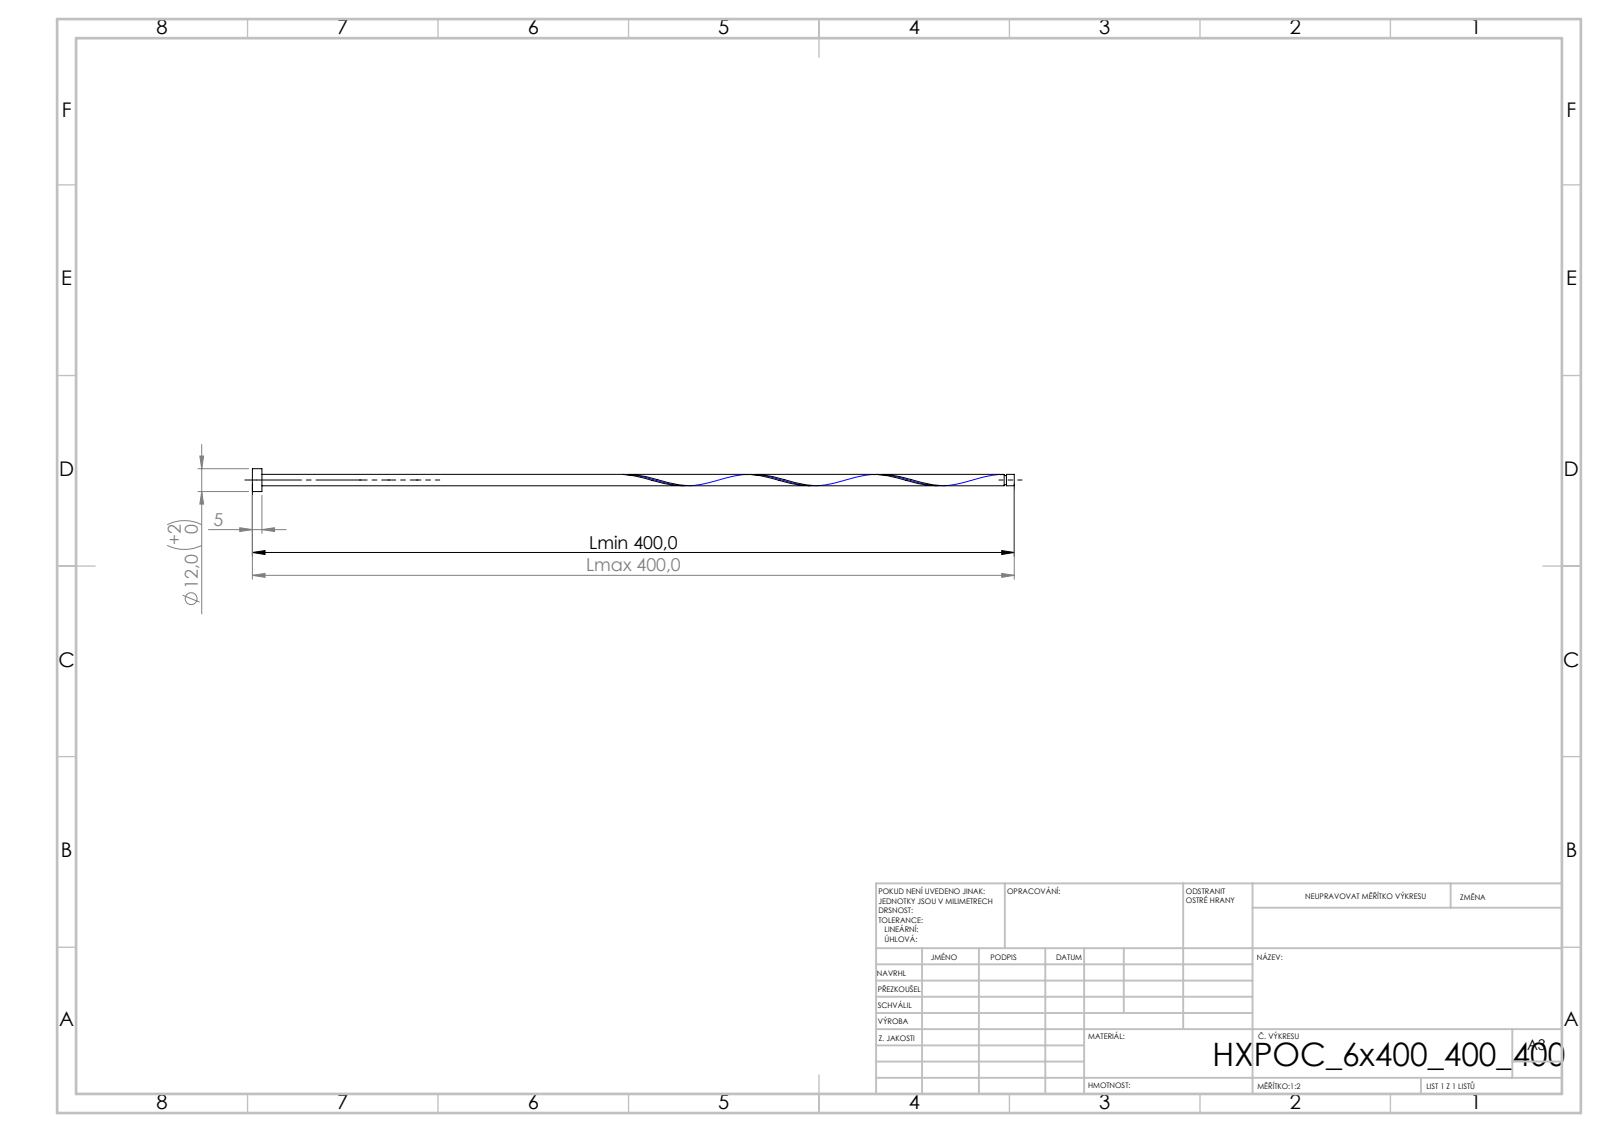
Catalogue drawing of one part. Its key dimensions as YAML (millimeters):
step_written_by: "SolidWorks 2019 (CONFIG_CONTROL_DESIGN)"
units: millimeters
bodies: {solids: 1, faces: 16, planar: 6, cylindrical: 9, other: 1}
overall_size: [400, 12, 12]
volume: 14128
surface_area: 10510
round_bosses_or_shafts:
  - {diameter: 12, count: 1}
  - {diameter: 6, count: 1}
  - {diameter: 4.8, count: 1}
face_to_face_distances: [5, 400, 395, 395.88, 390.88, 4.12, 394.68, 389.68, 1.2, 5.32]
